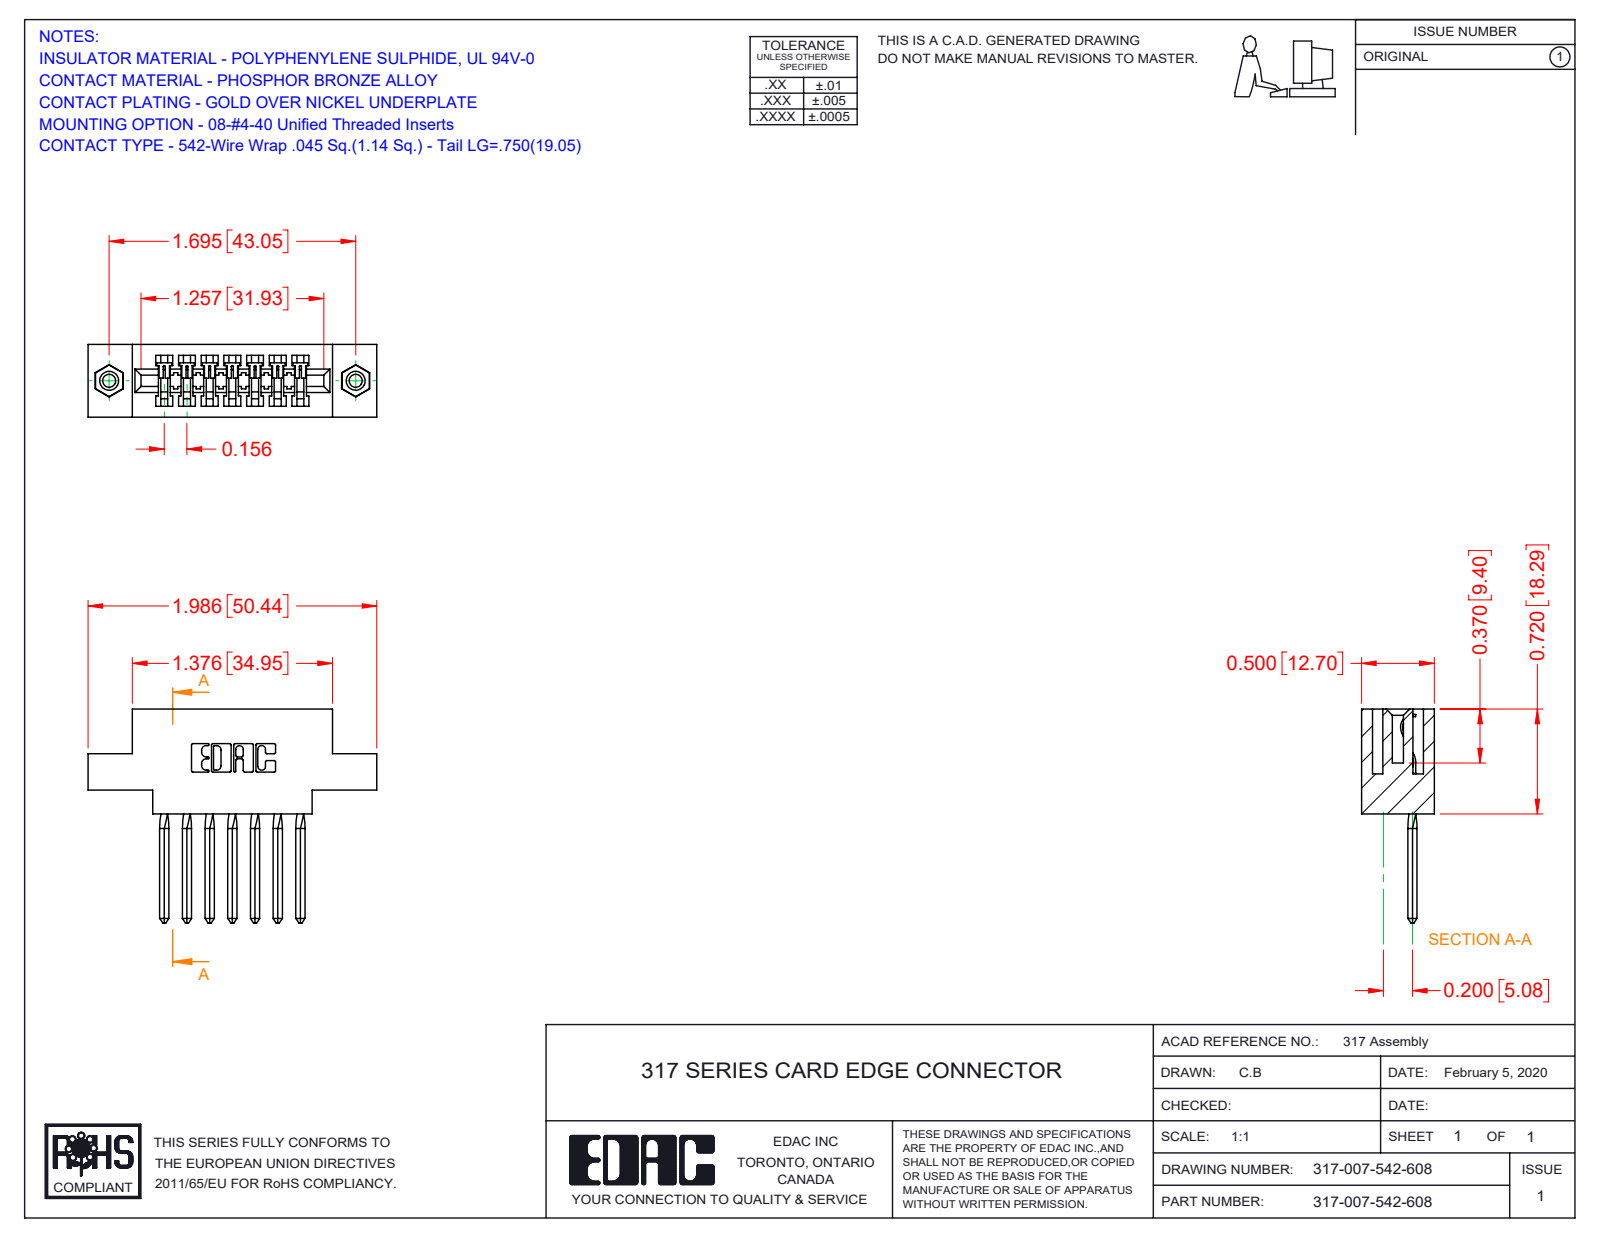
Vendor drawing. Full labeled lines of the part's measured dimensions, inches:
Part name (STEP PRODUCT): 317 Part_.156 Dia - TI; 345-250-001_345-250-003-102; 317-007-542-608; 317-290-003_542
STEP written by: SolidWorks 2016 (CONFIG_CONTROL_DESIGN)
Units: inches
Bodies: 10 solids, 687 faces (538 planar, 105 cylindrical, 44 other)
Overall size (bounding box): 1.986 × 1.47 × 0.5
Volume: 0.418 in³ · Surface area: 11.78 in²
Round holes (diameter × count): ⌀0.089 ×2, ⌀0.125 ×2, ⌀0.156 ×2
Round bosses / shafts (diameter × count): ⌀0.155 ×2
Partial cylindrical surfaces — rounded edges, fillets, slot ends (radius × count): R0.01 ×22, R0.006 ×14, R0.007 ×6, R0.031 ×6, R0.026 ×3, R0.074 ×1, R0.089 ×1, R0.1 ×1
Main face-to-face distances: 0.5, 0.075, 0.425, 0.11, 0.156, 0.065, 0.116, 0.22, 0.136, 0.163
Hole centre spacings: 1.695
